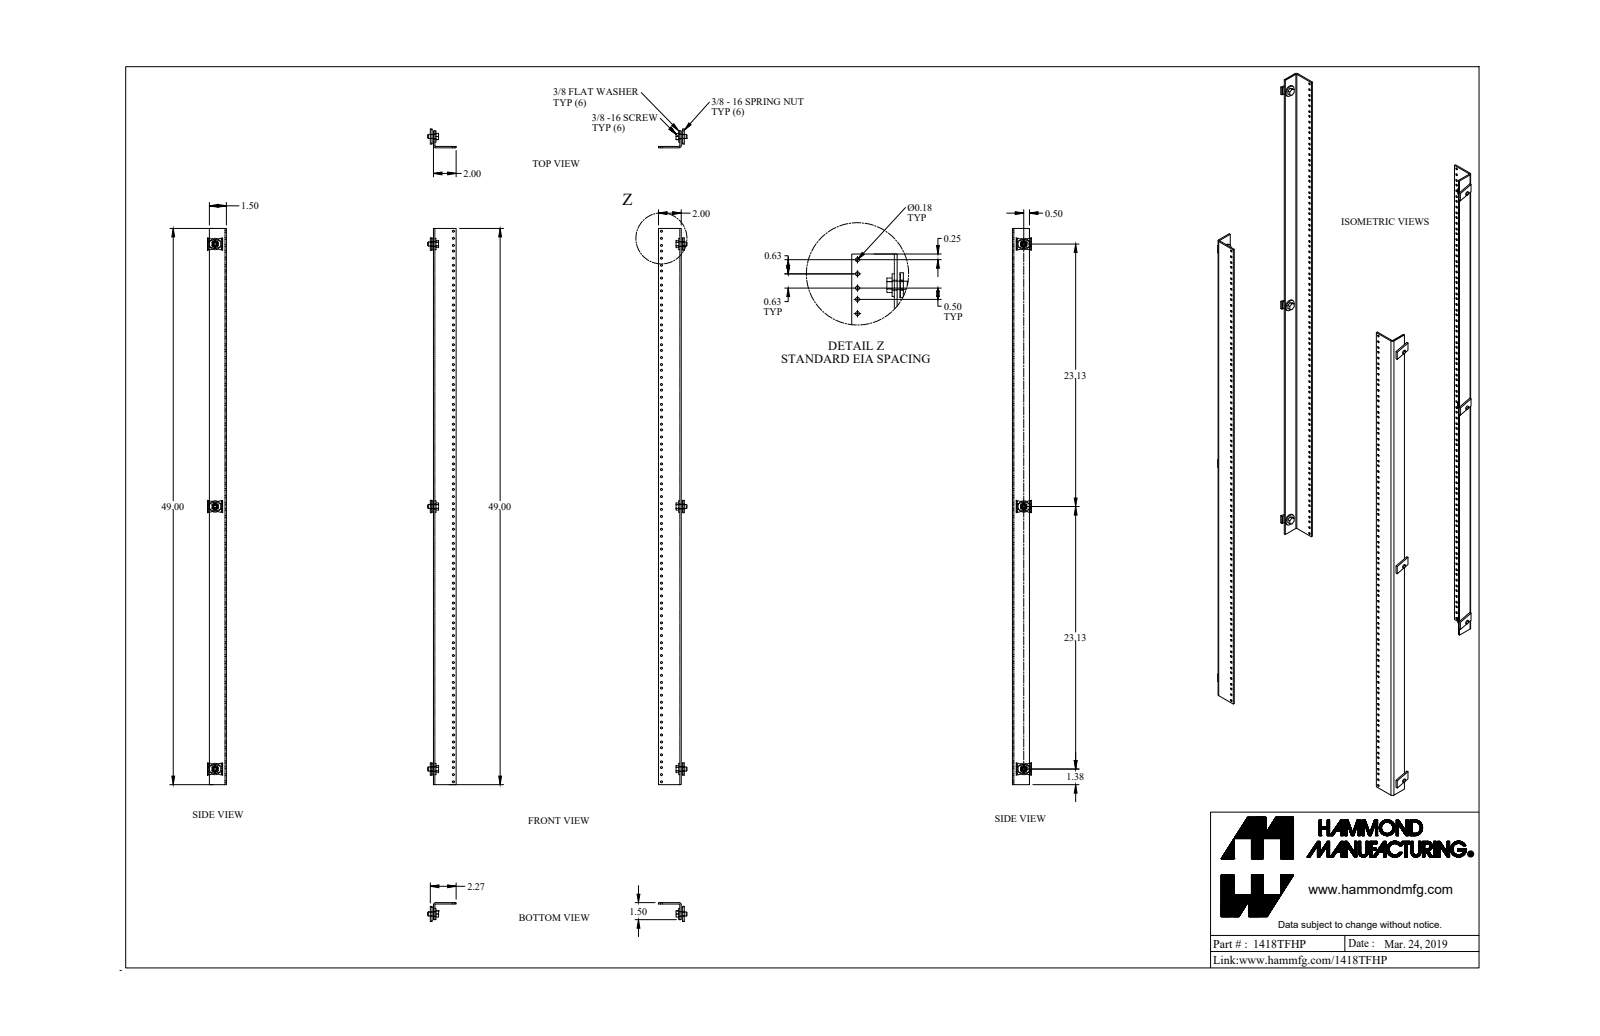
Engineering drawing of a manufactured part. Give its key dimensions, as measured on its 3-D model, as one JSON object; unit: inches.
{"part_name": "1418TFHP_Default", "step_written_by": "SolidWorks 2019 (CONFIG_CONTROL_DESIGN)", "units": "inches", "bodies": {"solids": 20, "faces": 590, "planar": 178, "cylindrical": 400, "other": 12}, "overall_size": [49, 22.856, 1.668], "volume_in3": 42.06, "surface_area_in2": 717.1, "round_holes": [[0.177, 168], [0.437, 4], [0.313, 3], [0.445, 3]], "round_bosses_or_shafts": [[1, 3], [0.36, 3]], "partial_cylinders_radius": [[0.06, 2], [0.185, 2]], "face_to_face_distances": [0.125, 0.125, 21.84, 21.59, 21.715, 21.715, 1.5, 1.375, 1.375, 2], "hole_center_spacings": [1.75, 3.5, 7, 5.25, 8.75, 0.5, 1.25, 10.5]}
